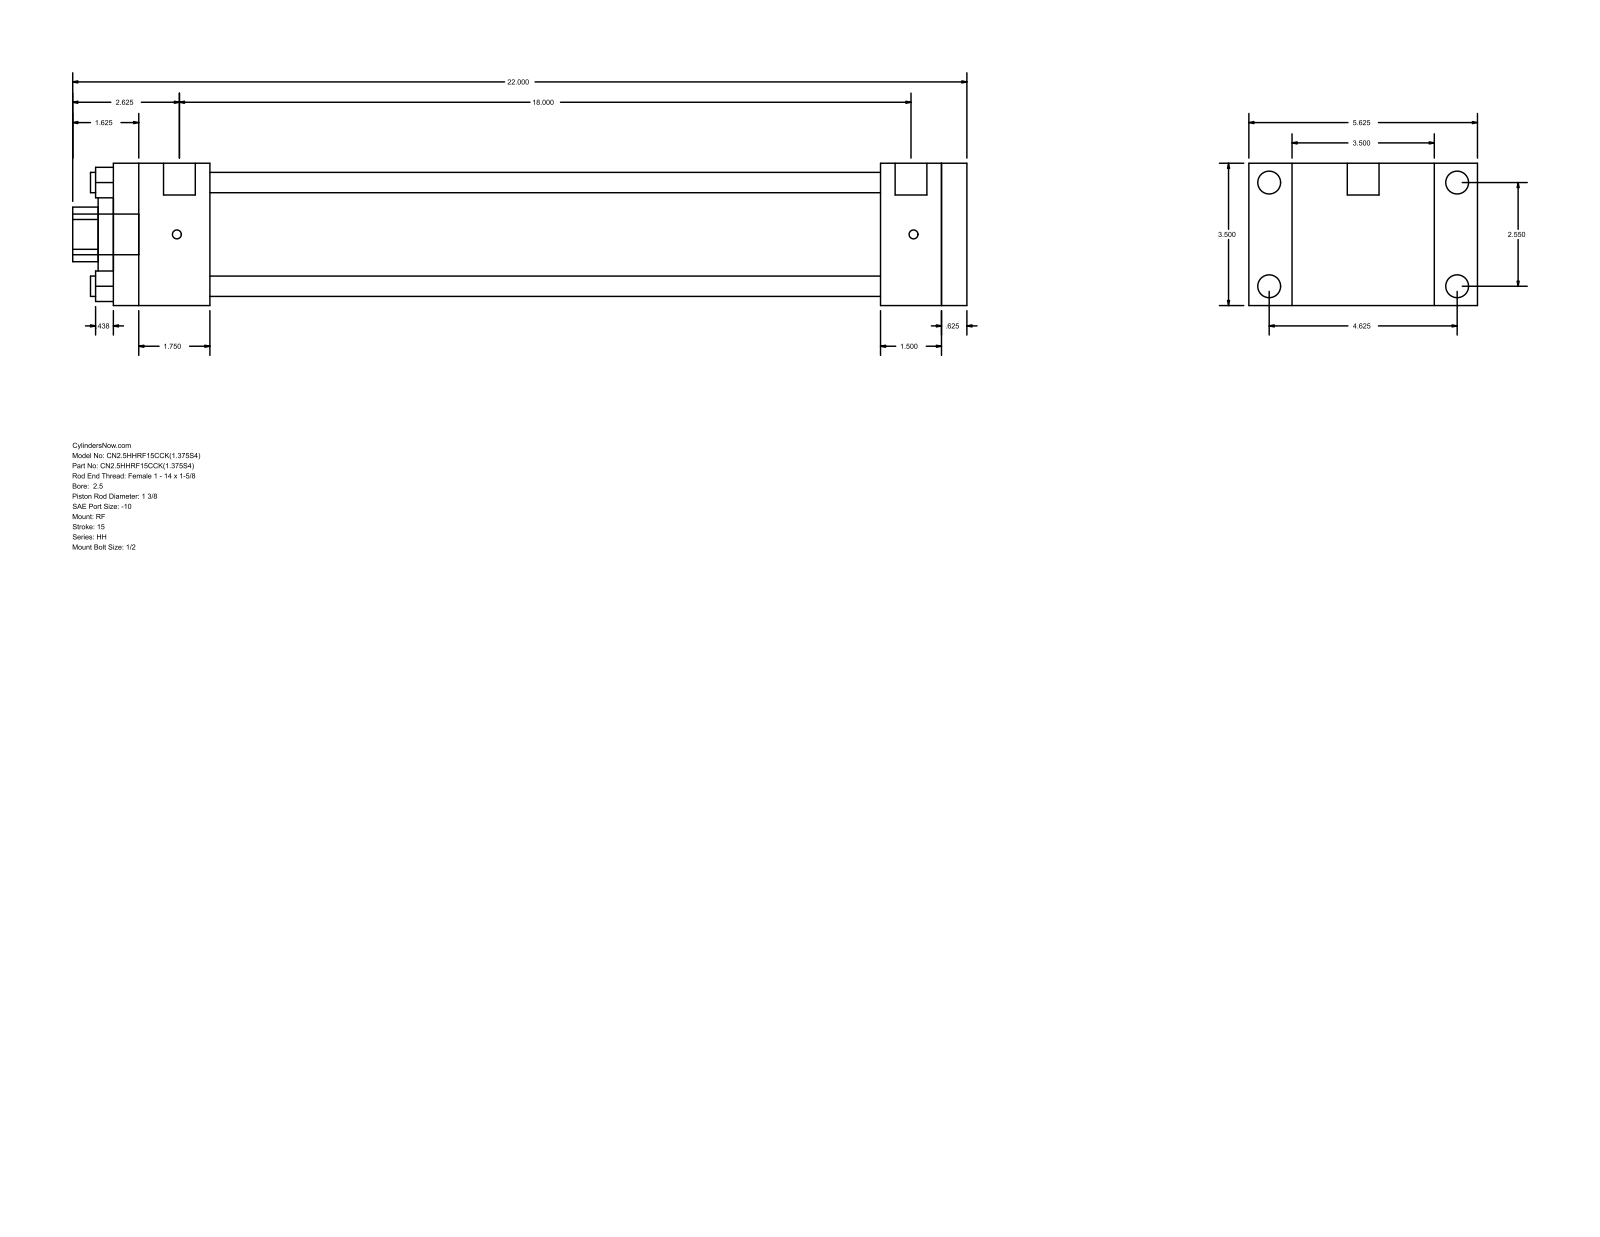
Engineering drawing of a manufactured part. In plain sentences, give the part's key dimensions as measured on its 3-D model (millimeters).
The part is named "HH_RF__0250_1.375". Its 3-D file was written by "GSSL Pune (CONFIG_CONTROL_DESIGN)". It is 0 solids with 92 faces: 64 planar, 28 cylindrical and 0 other. Overall it measures 558.8 by 142.88 by 88.9 millimeters. Round holes: 4 of diameter 12.7, 1 of diameter 34.92, 1 of diameter 50.8, 1 of diameter 73.03. Round bosses or shafts: 4 of diameter 14.3, 4 of diameter 5.56, 2 of diameter 19.84, 1 of diameter 25.4. Partial cylindrical surfaces (rounded edges, fillets, slot ends): 1 of radius 17.06. The main face-to-face distances are 88.9, 533.4, 15.88, 517.52, 60.32, 457.2, 473.08, 479.42, 419.1, 38.1. The hole center spacings are 45.79, 64.76, 91.58.
